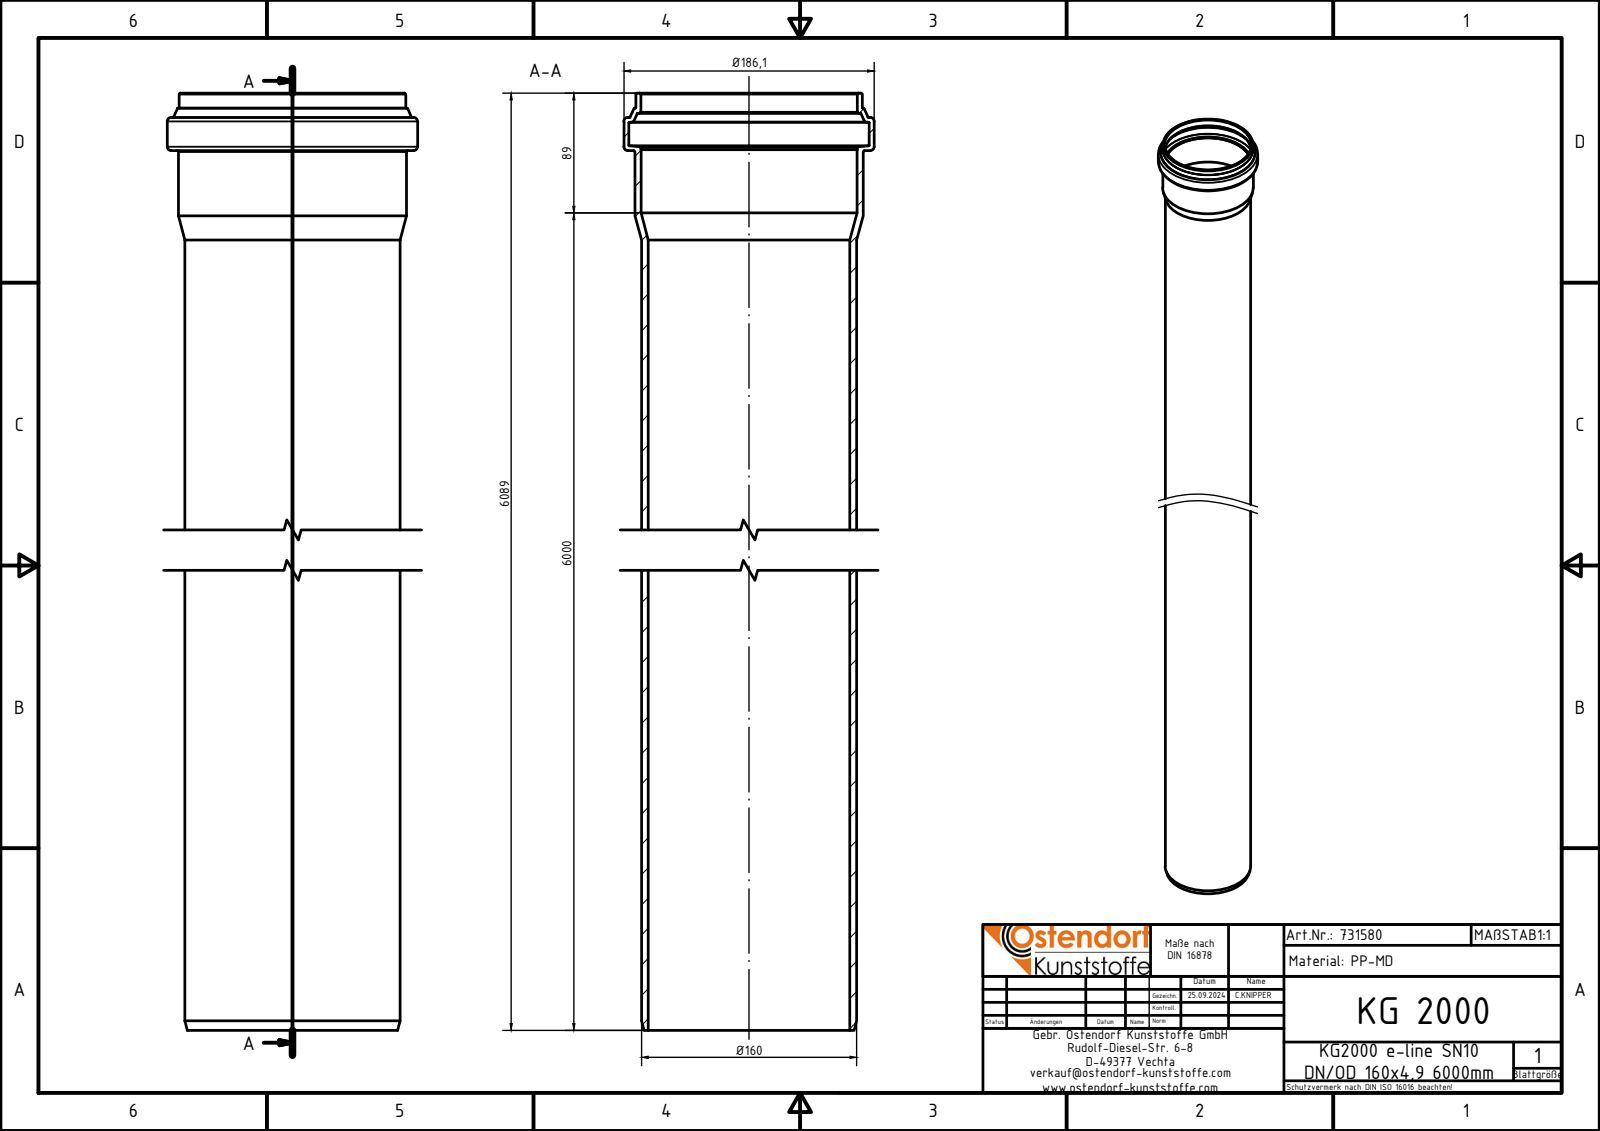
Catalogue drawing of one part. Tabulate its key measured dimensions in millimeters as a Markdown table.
| quantity | value |
| --- | --- |
| part name | 731580z |
| STEP written by | Autodesk Inventor 2024 (AUTOMOTIVE_DESIGN) |
| units | millimeters |
| bodies | 1 solid, 37 faces (6 planar, 9 cylindrical, 22 other) |
| overall size | 6089 × 186.1 × 186.1 |
| volume | 15 030 000 mm³ |
| surface area | 5 953 000 mm² |
| round holes (diameter × count) | 149.85 × 1, 160.6 × 1, 161 × 1, 178.7 × 1 |
| round bosses / shafts (diameter × count) | 186.1 × 1, 169.6 × 1, 168.4 × 1, 160 × 1 |
| main face-to-face distances | 6046.3, 6089, 42.7, 6071, 24.7, 18, 6077.91, 31.61, 6.91, 11.09 |
